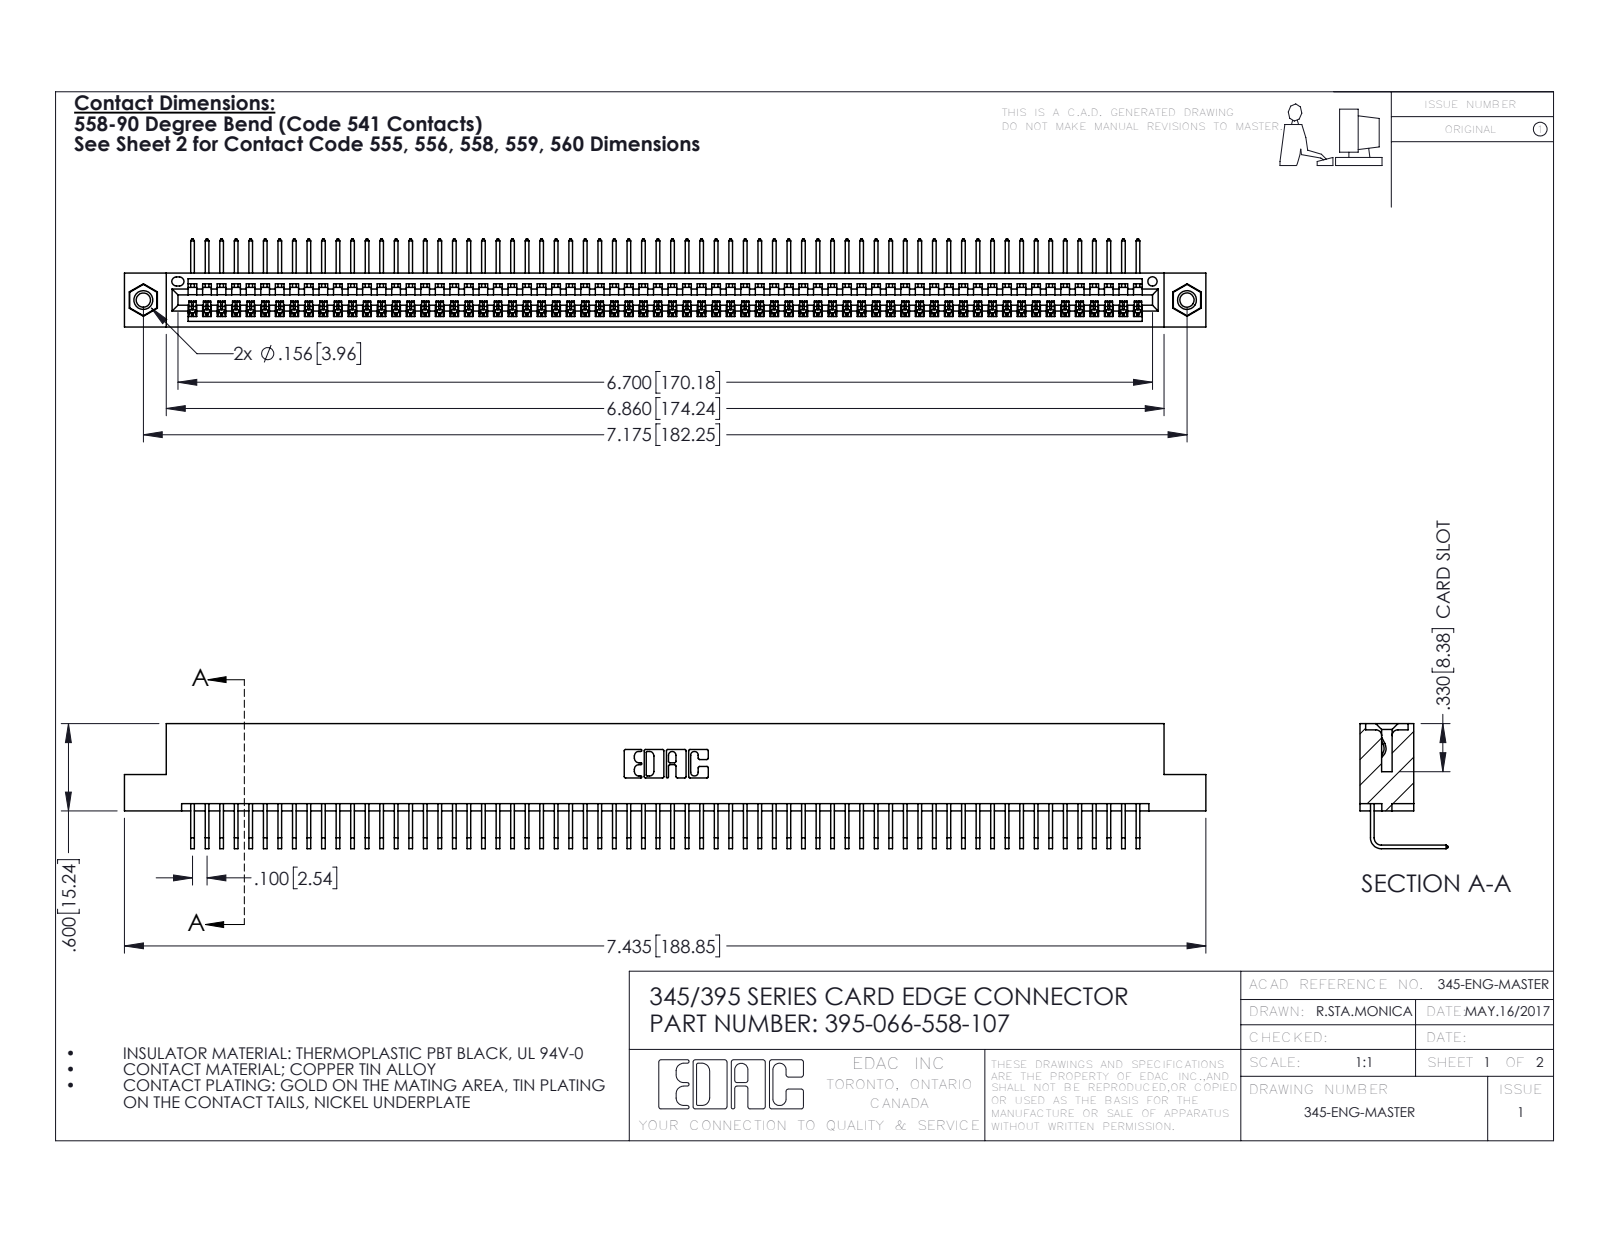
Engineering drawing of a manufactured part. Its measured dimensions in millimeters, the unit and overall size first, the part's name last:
Units: millimetres
Overall size (bounding box): 188.8 × 21.8 × 15.4
Round holes (diameter × count): ⌀2.5 ×2, ⌀3.2 ×2, ⌀4 ×2, ⌀1.6 ×1
Round bosses / shafts (diameter × count): ⌀3.9 ×2
Partial cylindrical surfaces — rounded edges, fillets, slot ends (radius × count): R0.2 ×132, R0.3 ×22, R0.2 ×6, R0.8 ×6, R0.7 ×3, R0.8 ×2, R1 ×2, R0.4 ×1
Main face-to-face distances: 1.8, 7.6, 9.4, 5.1, 2.5, 6.9, 0.6, 5.7, 3.8, 1.8
Hole centre spacings: 6.9, 176.3, 182.2
Volume: 18 340 mm³ · Surface area: 26 030 mm²
Bodies: 69 solids, 4146 faces (2884 planar, 1246 cylindrical, 16 other)
Part name (STEP PRODUCT): 345-250-001_345-250-005-103; 395-066-558-107; 345-292-001_558 Tail - 2; 345 Part_Flush Mounting Lugs - 0.156 Dia-TI
STEP written by: SolidWorks 2016 (CONFIG_CONTROL_DESIGN)
